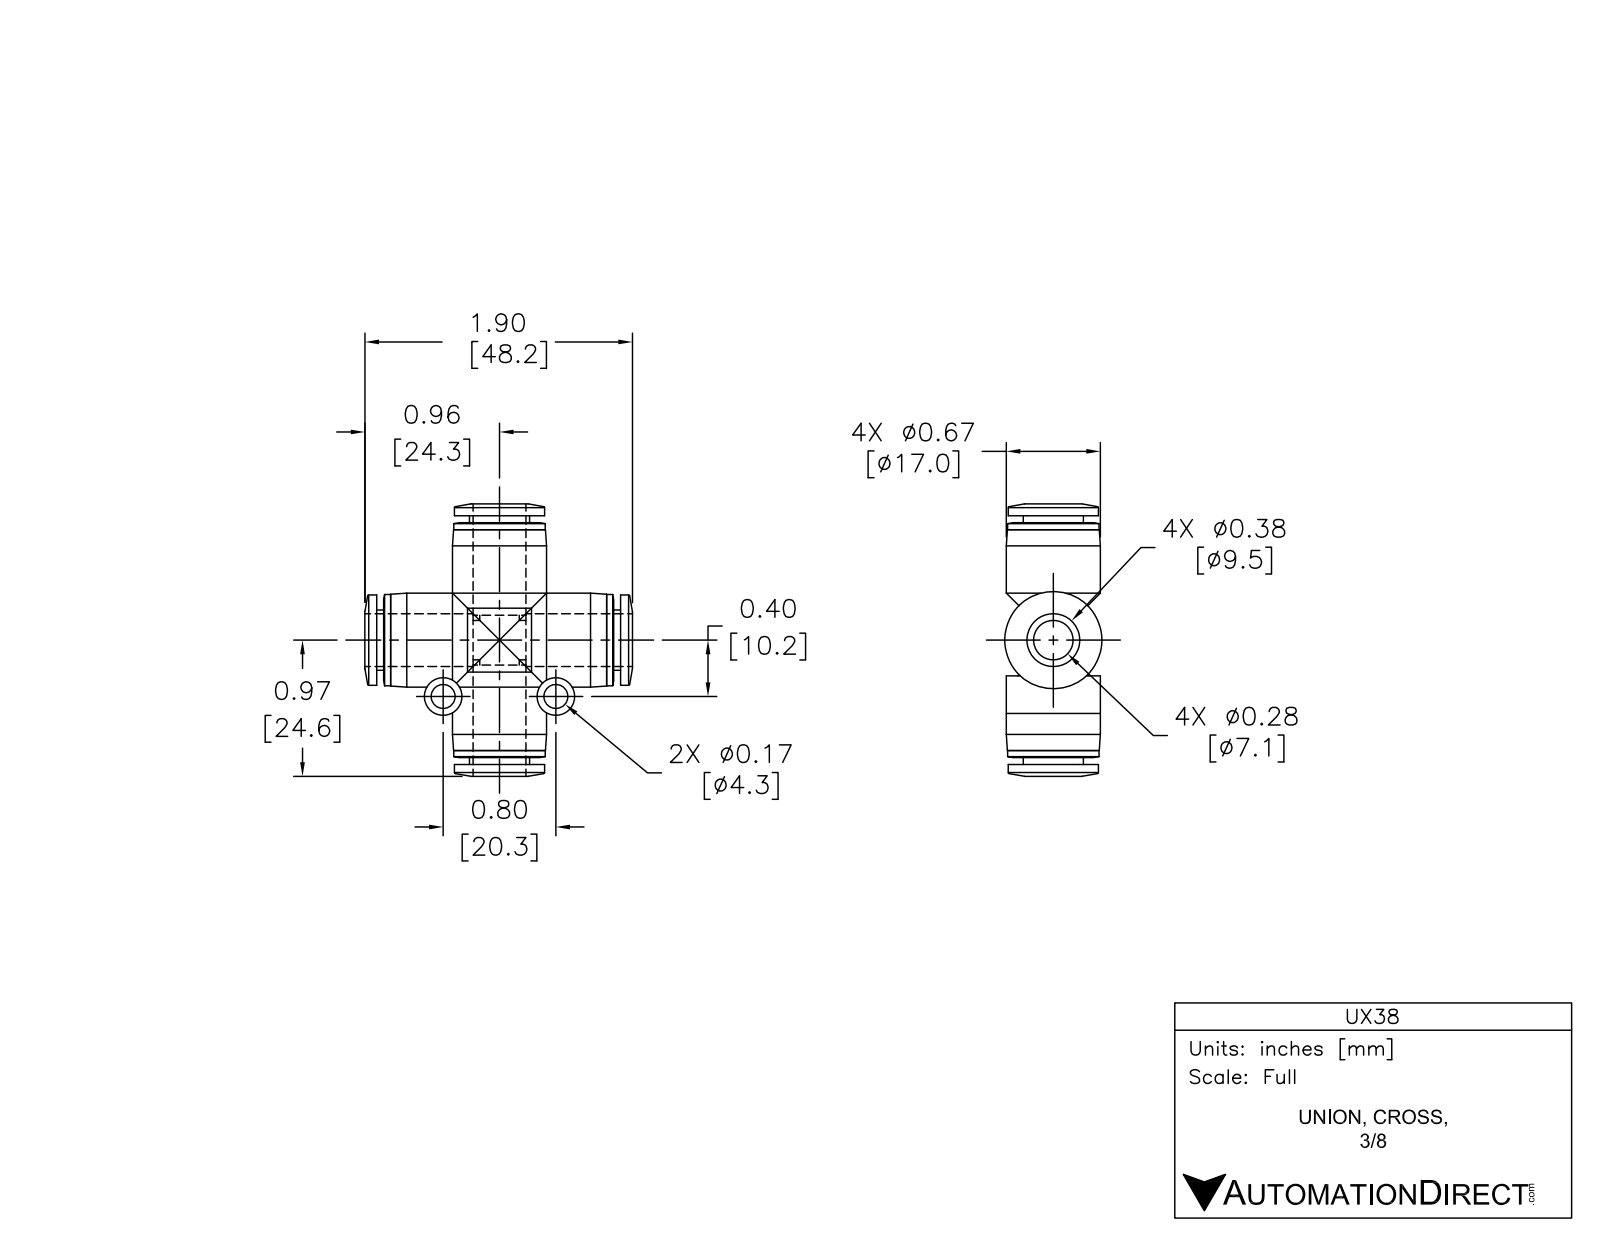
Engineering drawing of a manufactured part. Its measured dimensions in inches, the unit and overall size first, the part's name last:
Units: inches
Overall size (bounding box): 1.996 × 1.905 × 0.689
Round holes (diameter × count): ⌀0.169 ×2, ⌀0.315 ×2, ⌀0.386 ×1, ⌀0.396 ×1
Round bosses / shafts (diameter × count): ⌀0.689 ×2, ⌀0.669 ×2, ⌀0.661 ×2, ⌀0.441 ×2, ⌀0.276 ×2, ⌀0.469 ×1, ⌀0.46 ×1
Main face-to-face distances: 0.051, 1.772, 1.681, 1.823, 1.732, 0.63, 1.193, 0.579, 1.141, 0.685
Hole centre spacings: 0.799
Volume: 0.693 in³ · Surface area: 14.85 in²
Bodies: 1 solid, 122 faces (26 planar, 62 cylindrical, 34 other)
Part name (STEP PRODUCT): UX38
STEP written by: SolidWorks 2018 (AUTOMOTIVE_DESIGN)
